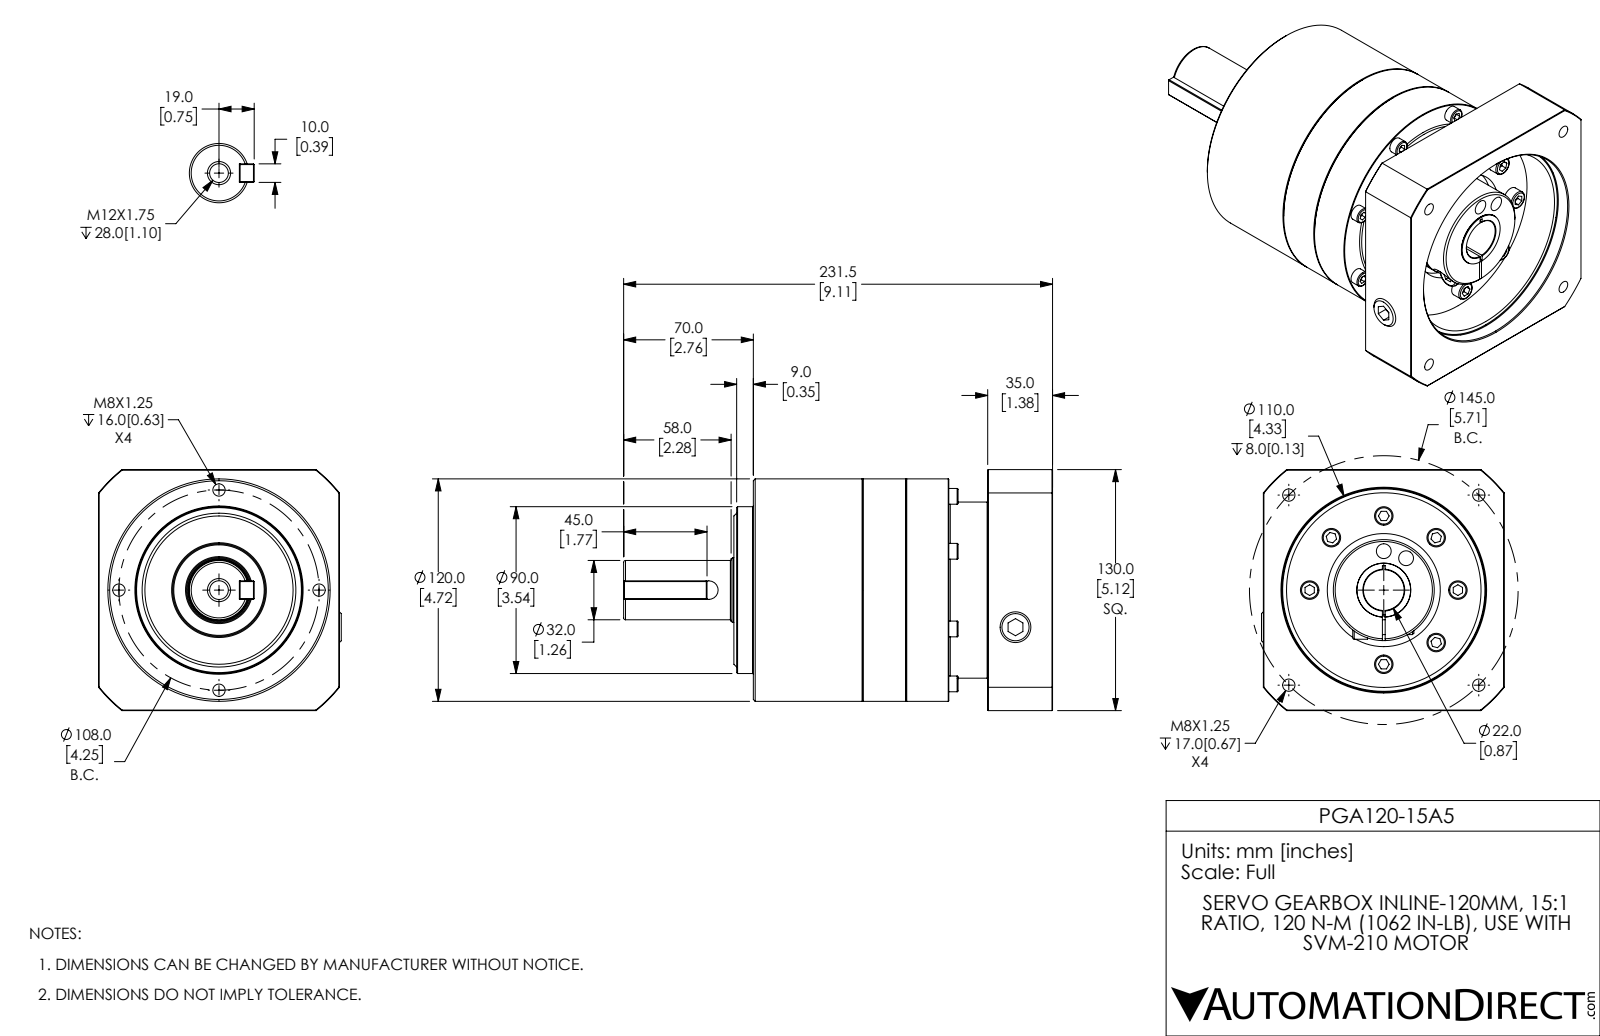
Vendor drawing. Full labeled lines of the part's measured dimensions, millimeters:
Part name (STEP PRODUCT): PGA120-15A5
STEP written by: SolidWorks 2019 (CONFIG_CONTROL_DESIGN)
Units: millimetres
Bodies: 1 solid, 448 faces (193 planar, 101 cylindrical, 154 other)
Overall size (bounding box): 231.5 × 131 × 130
Volume: 1 780 000 mm³ · Surface area: 145 362 mm²
Round holes (diameter × count): ⌀6.65 ×8, ⌀8 ×2, ⌀8.8 ×1, ⌀10.11 ×1, ⌀14.25 ×1, ⌀22 ×1, ⌀61 ×1, ⌀105 ×1, ⌀110 ×1
Round bosses / shafts (diameter × count): ⌀8.5 ×8, ⌀10 ×7, ⌀120 ×1, ⌀95 ×1, ⌀90 ×1, ⌀54.5 ×1, ⌀35 ×1, ⌀32 ×1
Partial cylindrical surfaces — rounded edges, fillets, slot ends (radius × count): R3.32 ×1, R5 ×1, R7 ×1, R83.5 ×1
Main face-to-face distances: 130, 35, 6, 29, 161.5, 132.5, 126.5, 27, 21, 172
Hole centre spacings: 51.34, 117.09, 54, 72.51, 76.37, 102.54, 21, 57.94
